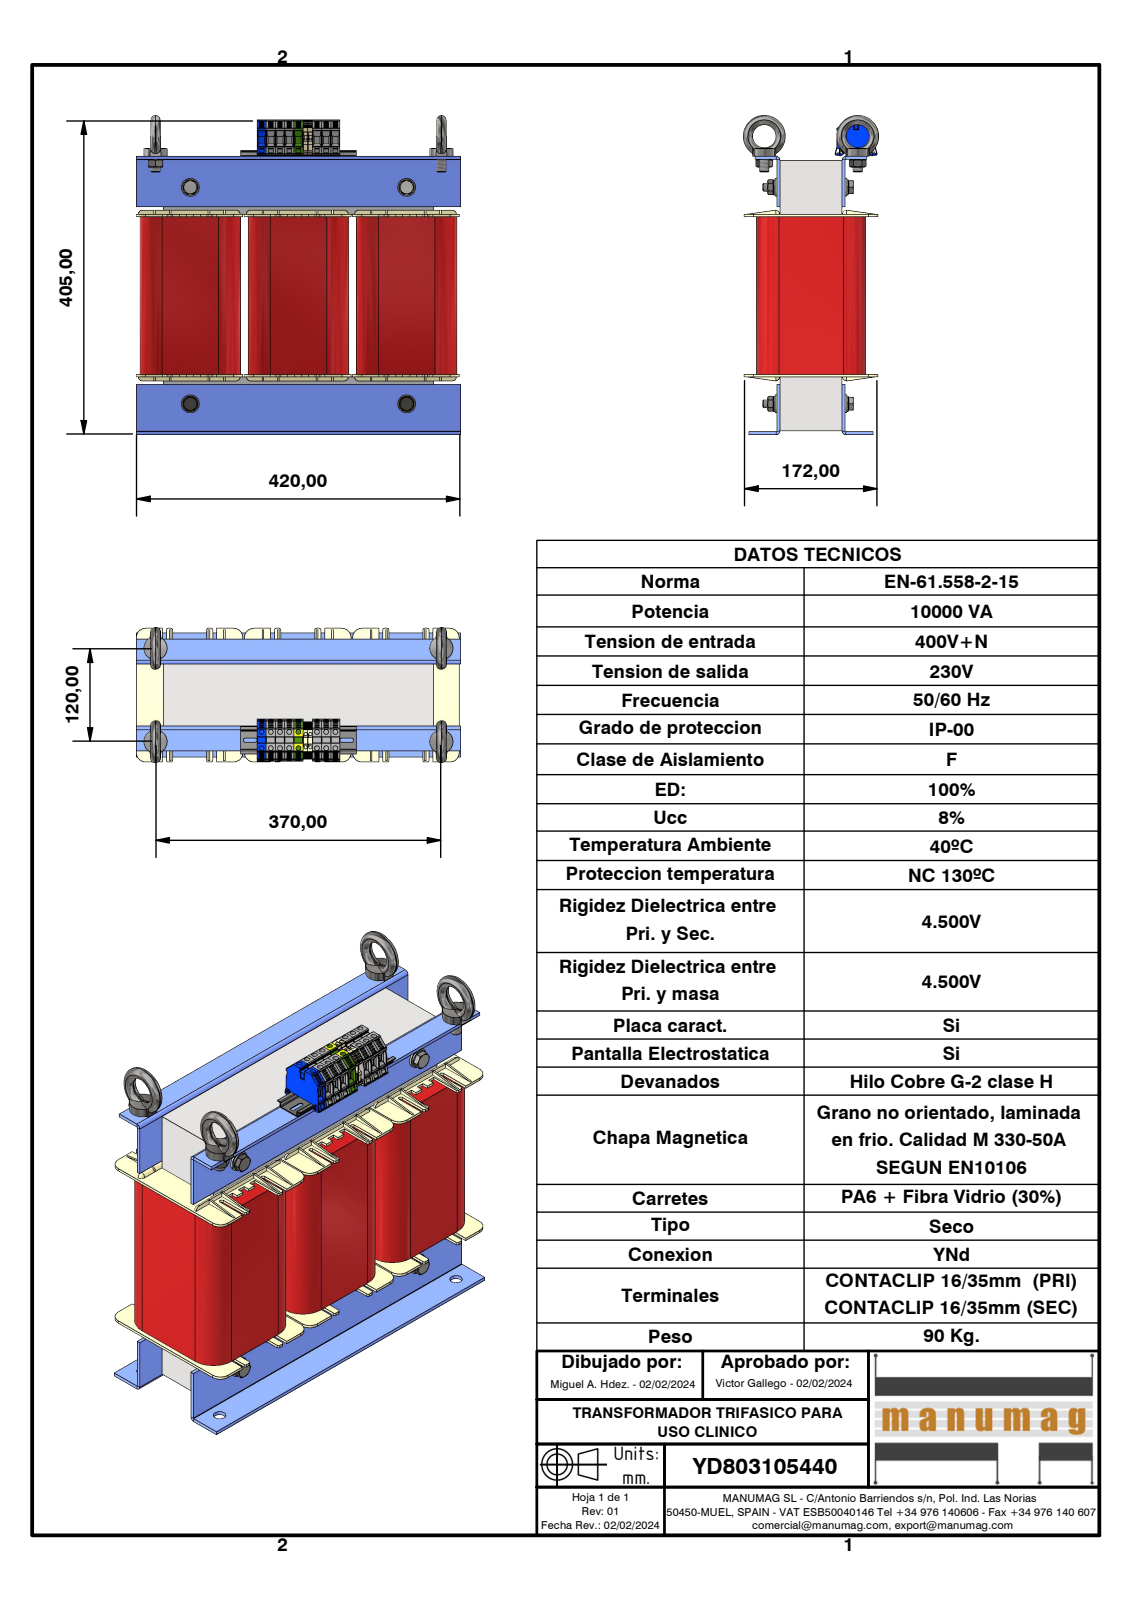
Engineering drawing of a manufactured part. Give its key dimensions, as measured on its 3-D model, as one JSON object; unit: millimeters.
{"part_name": "YD803105440; 3UI210 350 x 350 - 80; UI 210_80_BOBINADO; RC70 NT070 INFERIOR (+8 more)", "step_written_by": "Autodesk Inventor 2023 (AUTOMOTIVE_DESIGN)", "units": "millimeters", "bodies": {"solids": 49, "faces": 5498, "planar": 3258, "cylindrical": 1788, "other": 452}, "overall_size": [467, 413, 174], "volume_mm3": 15680000, "surface_area_mm2": 1966000, "round_holes": [[6.3, 16], [13, 6], [15, 6], [4.3, 4], [8.38, 4], [10, 4], [10.5, 4], [14, 4], [2.4, 2], [2.5, 2], [2.75, 2], [2.95, 2]], "round_bosses_or_shafts": [[23, 4], [20, 4], [15.4, 4], [12, 4], [11.5, 4], [10.8, 4], [9.19, 4], [54, 2]], "partial_cylinders_radius": [[0.3, 383], [2, 39], [0.25, 32], [1, 18], [0.5, 13], [2.5, 12], [2.6, 12], [2.92, 12]], "face_to_face_distances": [140, 70, 280, 84, 4, 210, 80, 3, 26.5, 113.5], "hole_center_spacings": [11.9, 24.14, 21, 23.8, 31.74, 47.9, 52.3, 59.8]}
